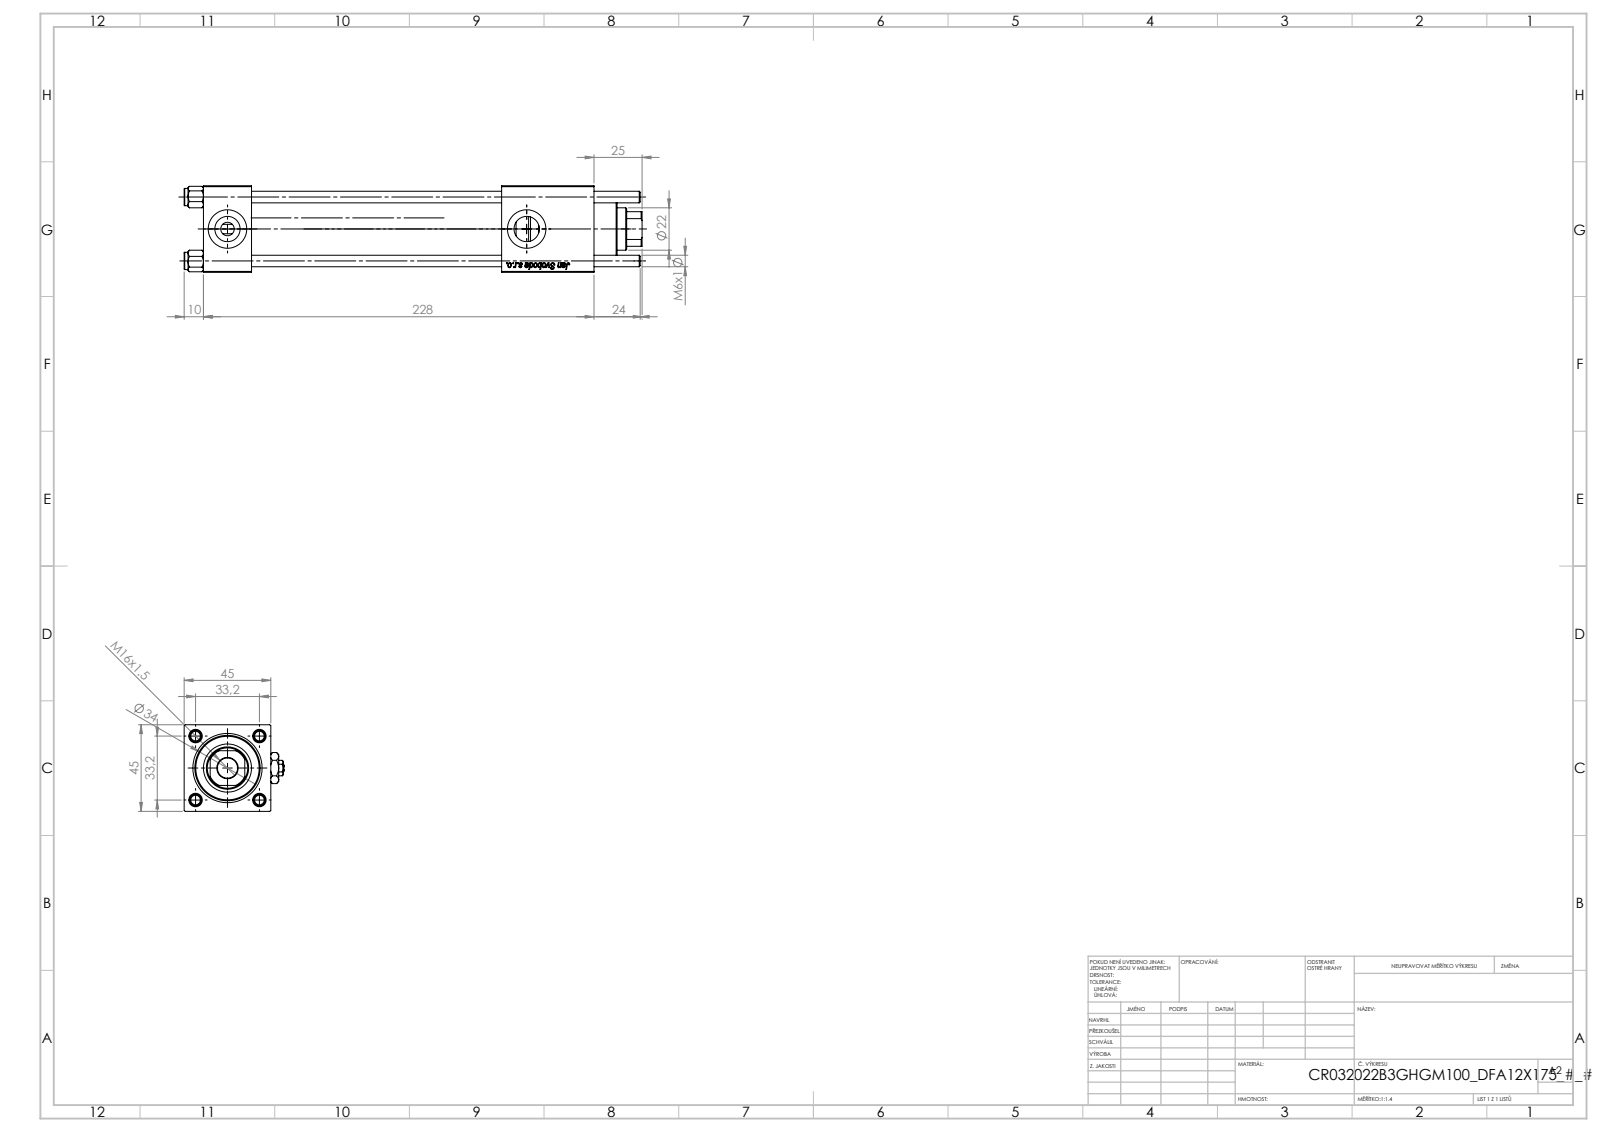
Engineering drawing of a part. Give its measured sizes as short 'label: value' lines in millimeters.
name: V215_VC_A; V215CR_VCP_B; FEMALE_PART_FOR_DFA; Zatka_pro_OIL_PORT (+3 more)
written by: SolidWorks 2019 (CONFIG_CONTROL_DESIGN)
unit: mm
bodies: 14 solids, 1289 faces (490 planar, 97 cylindrical, 702 other)
size: 238 × 52 × 45
volume: 288 441 mm³; area: 112 208 mm²
holes: 4× ⌀6, 2× ⌀7, 2× ⌀13.16, 2× ⌀20, 1× ⌀10.5, 1× ⌀22, 1× ⌀24, 1× ⌀25, 1× ⌀32, 1× ⌀33
bosses: 4× ⌀9, 1× ⌀38, 1× ⌀34, 1× ⌀28, 1× ⌀12, 1× ⌀10
rounds: 1× R9.75, 1× R10.5
face distances: 45, 25, 203, 155, 130, 44.8, 178, 48, 174.3, 149.3
hole spacings: 23.48, 33.2, 46.95, 155.5
